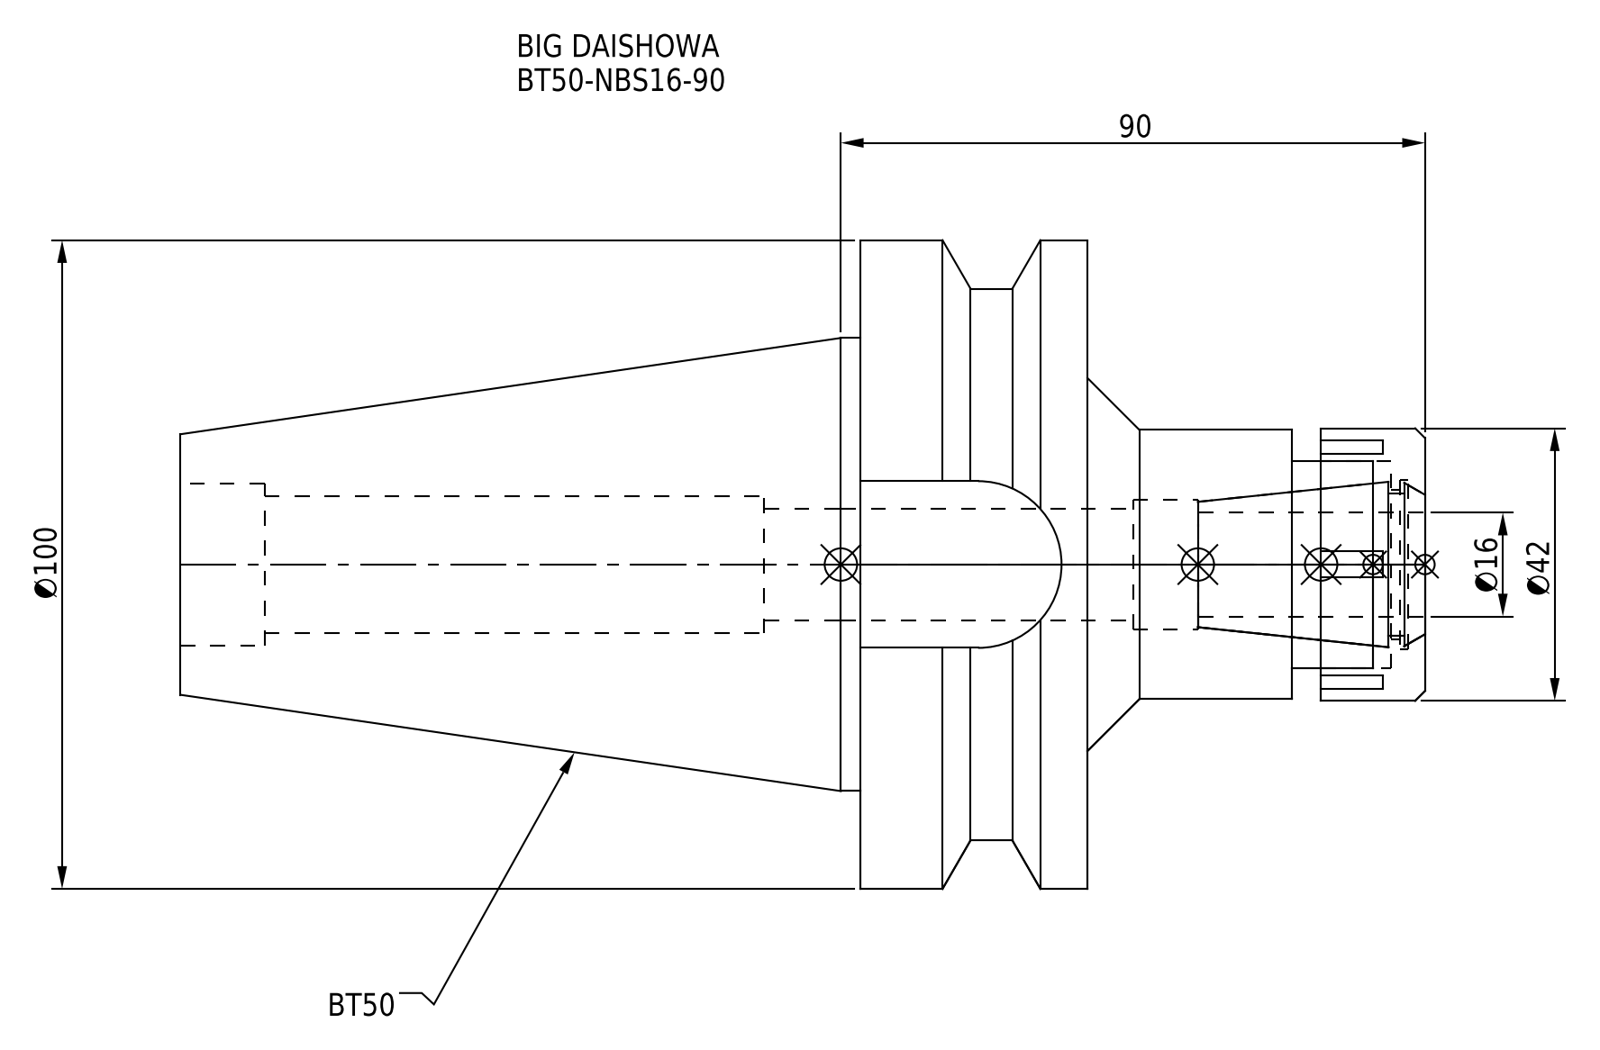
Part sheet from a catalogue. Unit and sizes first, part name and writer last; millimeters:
Units: millimetres
Overall size (bounding box): 191.8 × 100 × 100
Round holes (diameter × count): ⌀17.3 ×1, ⌀20 ×1, ⌀21.2 ×1, ⌀23 ×1, ⌀25 ×1, ⌀26 ×1, ⌀32 ×1
Round bosses / shafts (diameter × count): ⌀100 ×1, ⌀85 ×1, ⌀69.85 ×1, ⌀42 ×1, ⌀41.5 ×1
Partial cylindrical surfaces — rounded edges, fillets, slot ends (radius × count): R12.85 ×1
Main face-to-face distances: 35, 52, 87, 191.8, 139.8, 104.8, 70.8, 8, 20.5, 31.5
Volume: 501 347 mm³ · Surface area: 67 036 mm²
Bodies: 2 solids, 90 faces (44 planar, 32 cylindrical, 14 other)
Part name (STEP PRODUCT): DXF_TEMP_ASSY_ASM_4_ASM.stp; BT50-NBS16-90; BT50-NBS16-90_1.stp; BT50-NBS16-90.stp (+3 more)
STEP written by: SolidWorks 2019 (CONFIG_CONTROL_DESIGN)
